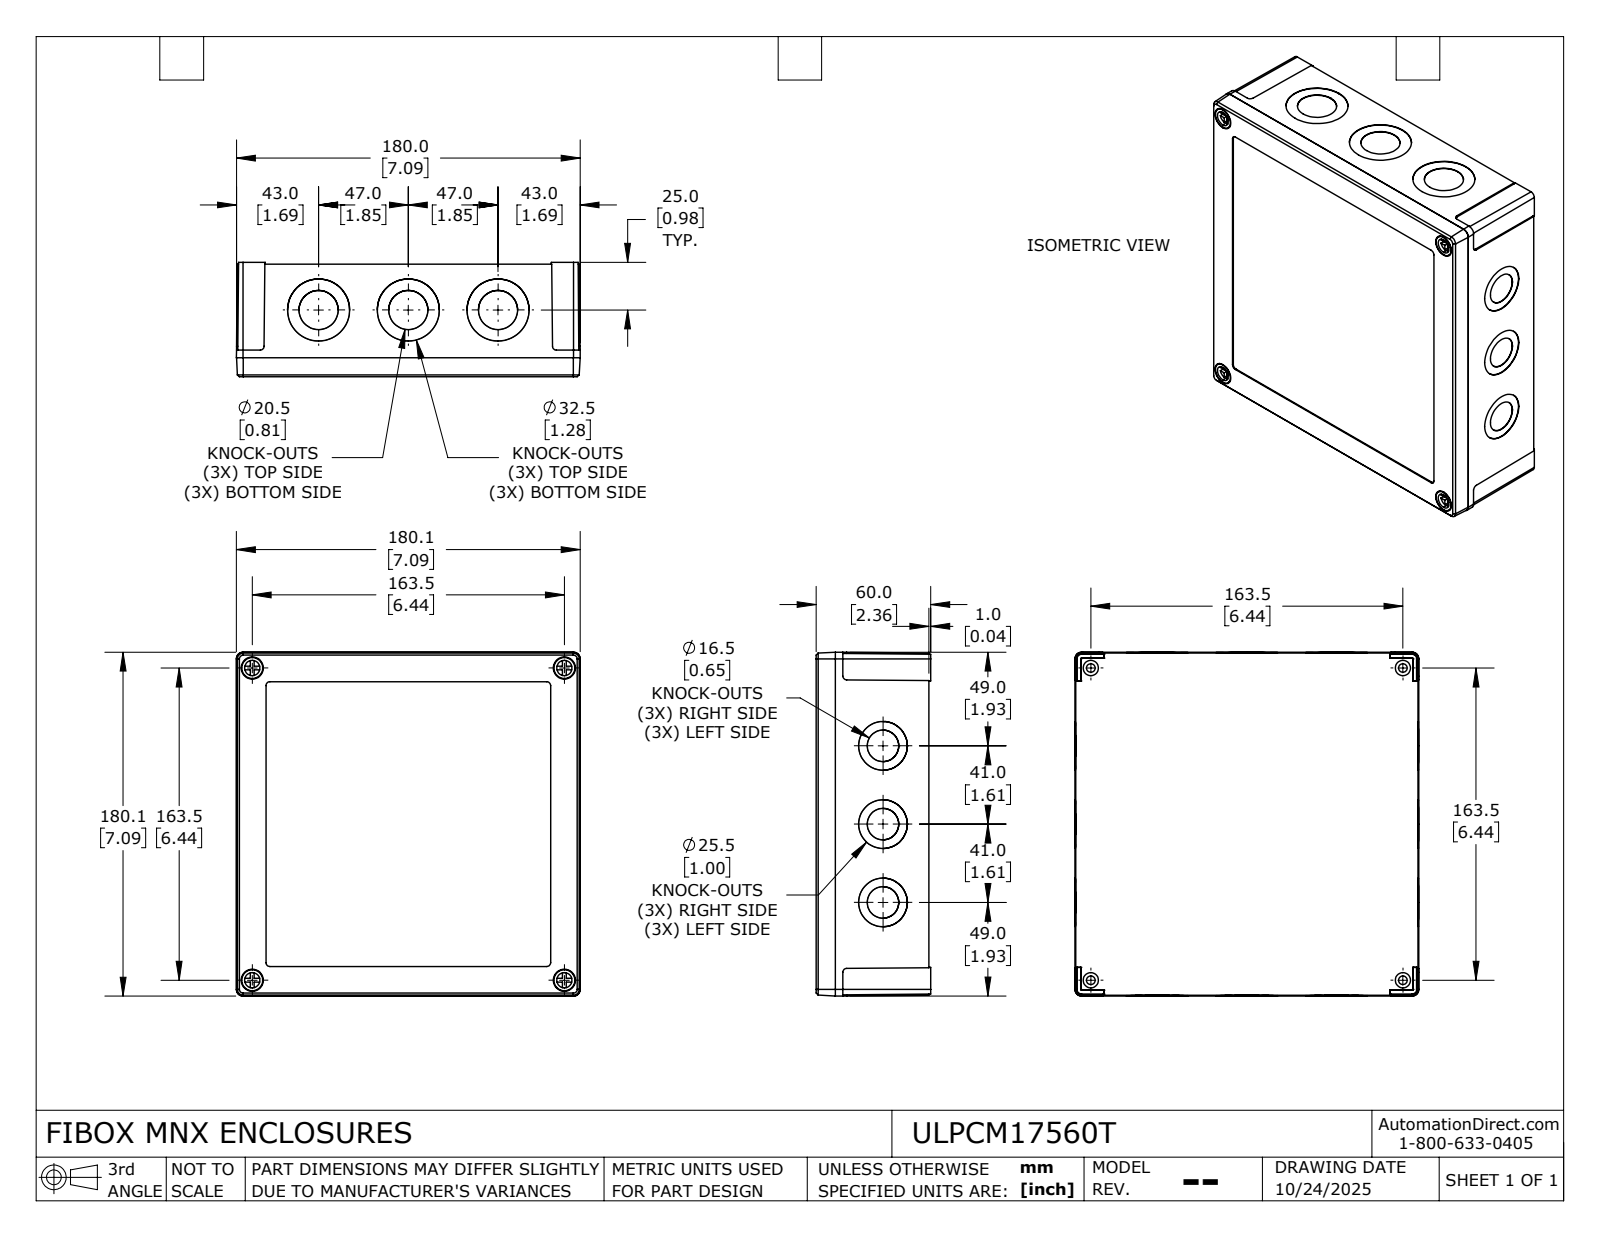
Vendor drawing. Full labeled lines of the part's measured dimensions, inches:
Part name (STEP PRODUCT): ULPCM17560T_Default
STEP written by: SolidWorks 2024 (CONFIG_CONTROL_DESIGN)
Units: inches
Bodies: 6 solids, 582 faces (318 planar, 224 cylindrical, 40 other)
Overall size (bounding box): 7.091 × 7.091 × 2.362
Volume: 21.68 in³ · Surface area: 342.9 in²
Round holes (diameter × count): ⌀0.126 ×12, ⌀0.157 ×12, ⌀0.65 ×6, ⌀0.807 ×6, ⌀1.004 ×6, ⌀1.28 ×6, ⌀0.177 ×4, ⌀0.315 ×4, ⌀0.457 ×4
Round bosses / shafts (diameter × count): ⌀0.315 ×12, ⌀0.098 ×8, ⌀0.433 ×4, ⌀0.283 ×4
Partial cylindrical surfaces — rounded edges, fillets, slot ends (radius × count): R0.079 ×8, R0.112 ×6, R0.042 ×4, R0.197 ×4, R0.046 ×2
Main face-to-face distances: 2.205, 0.118, 2.087, 0.098, 2.303, 2.185, 0.165, 2.323, 0.02, 0.276
Hole centre spacings: 1.333, 1.969, 2.866, 3.252, 4.79, 5.207, 5.469, 5.853
